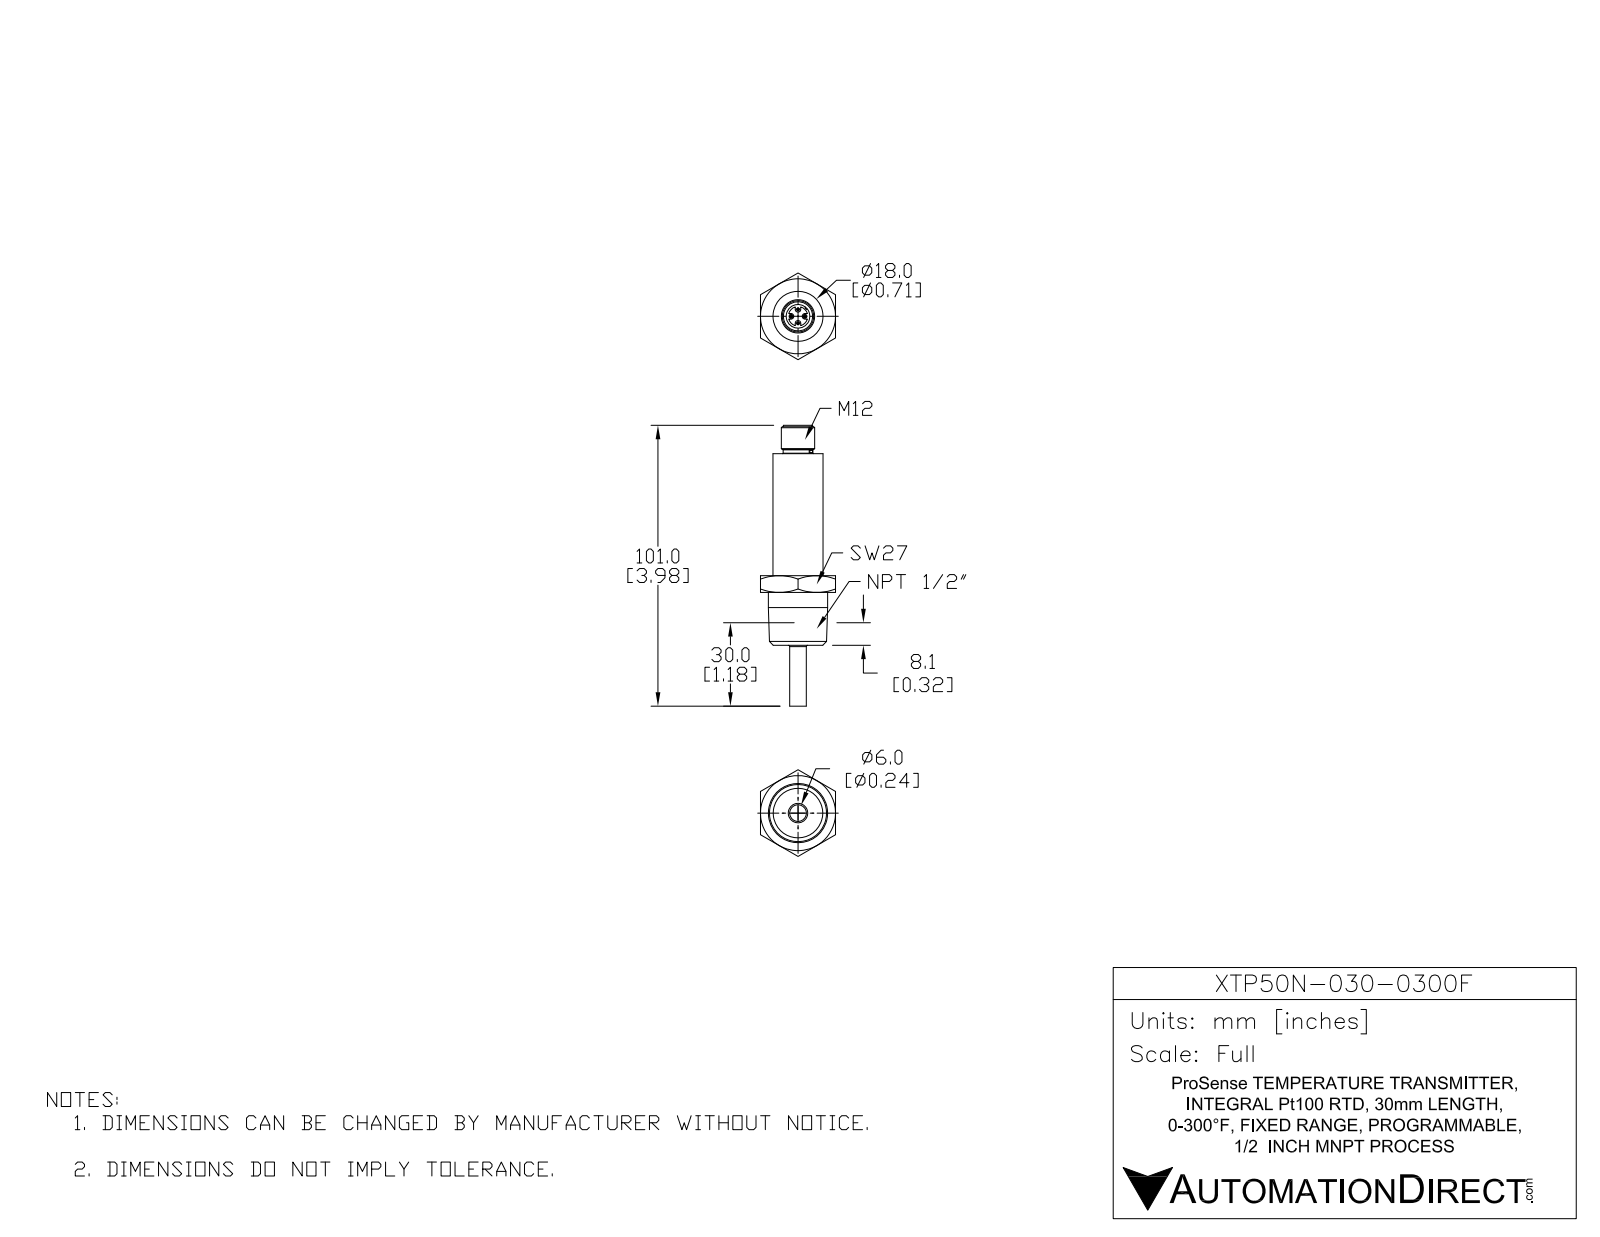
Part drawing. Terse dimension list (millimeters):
name: XTP50N-030-0300F
written by: SolidWorks 2015 (AUTOMOTIVE_DESIGN)
unit: mm
bodies: 1 solid, 117 faces (43 planar, 34 cylindrical, 40 other)
size: 101 × 31.18 × 27
volume: 22 355 mm³; area: 6 897 mm²
holes: 1× ⌀4, 1× ⌀8.5
bosses: 4× ⌀1.02, 1× ⌀21.34, 1× ⌀18, 1× ⌀12, 1× ⌀10.7, 1× ⌀10.5, 1× ⌀6
rounds: 4× R1, 1× R3.5, 1× R4.25
face distances: 27, 25, 19, 6, 68.9, 49.9, 43.9, 79.1, 60.1, 54.1
